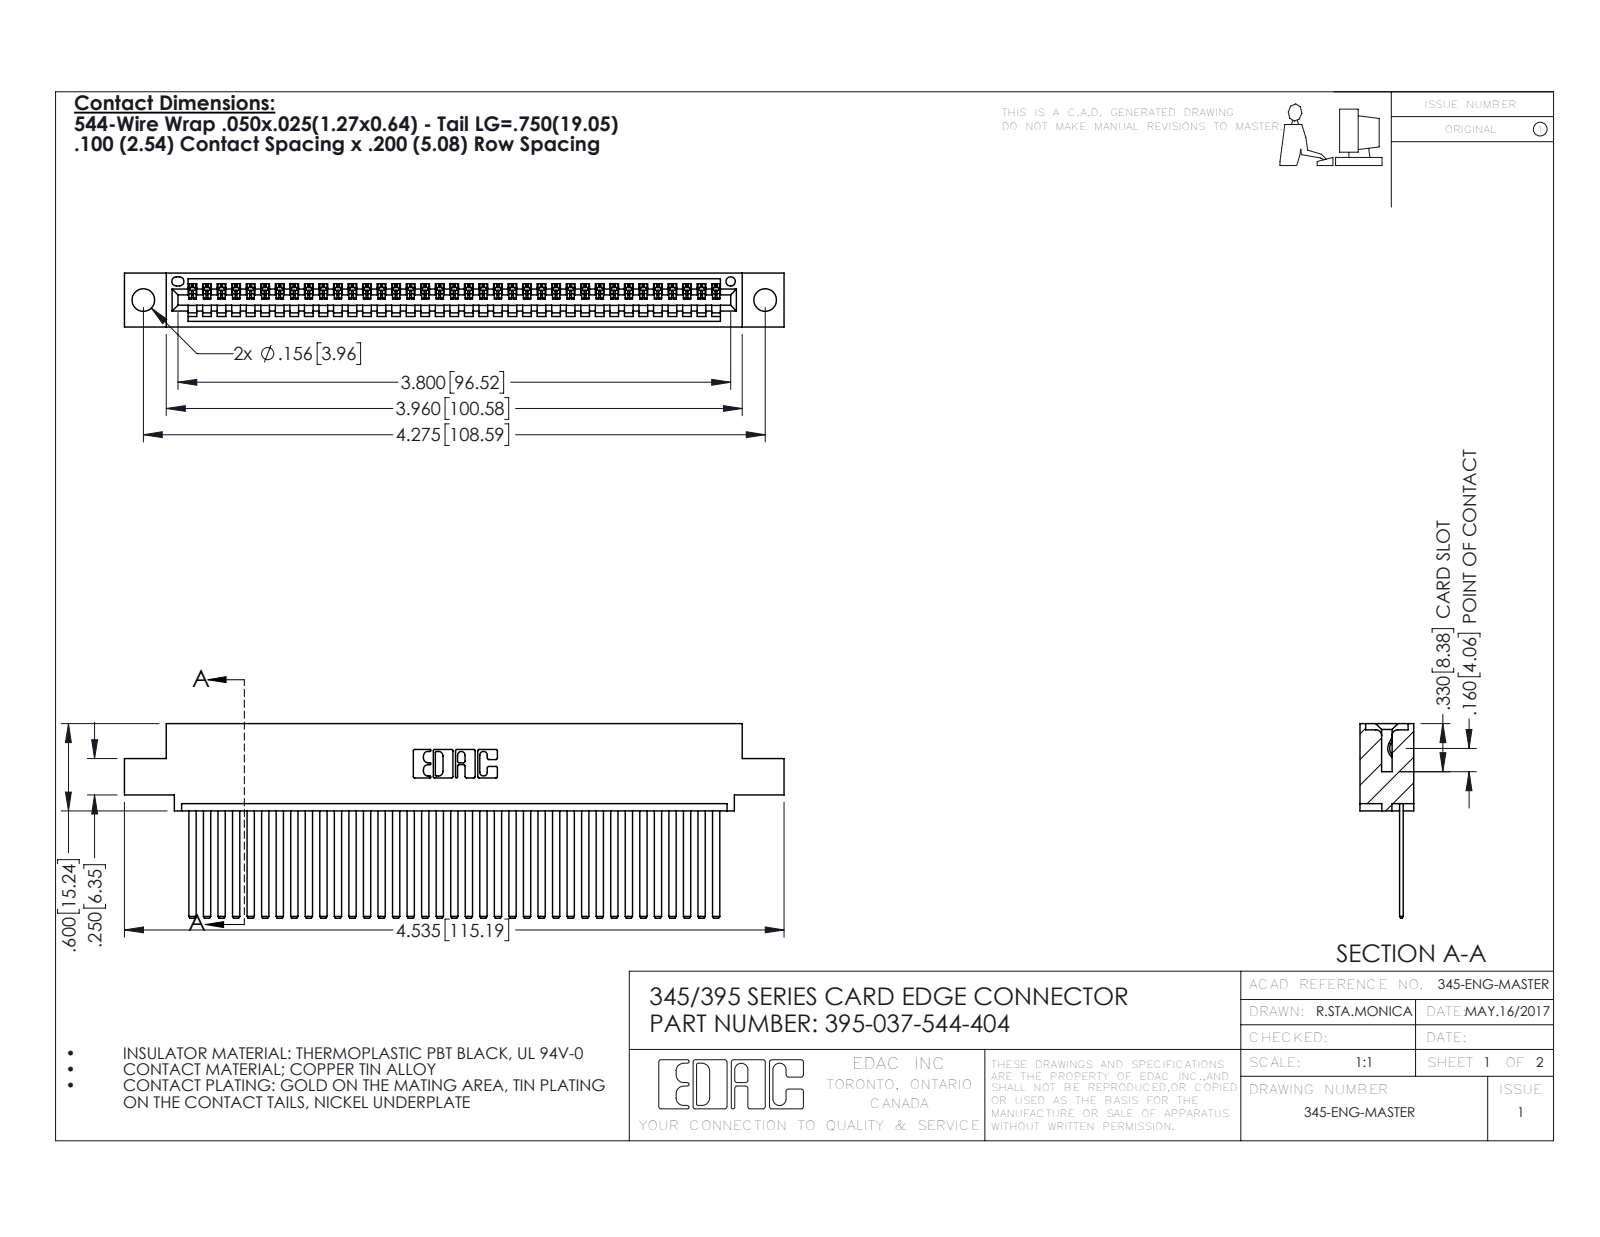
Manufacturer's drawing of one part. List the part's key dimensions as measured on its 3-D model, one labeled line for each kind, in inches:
Part name (STEP PRODUCT): 395-037-544-404; 345-292-001_345-293-144; 345 Part_0.110 Offset - 0.156 Dia-TH
STEP written by: SolidWorks 2016 (CONFIG_CONTROL_DESIGN)
Units: inches
Bodies: 38 solids, 2054 faces (1416 planar, 638 cylindrical, 0 other)
Overall size (bounding box): 4.535 × 1.337 × 0.37
Volume: 0.681 in³ · Surface area: 24.72 in²
Round holes (diameter × count): ⌀0.156 ×2, ⌀0.064 ×1
Partial cylindrical surfaces — rounded edges, fillets, slot ends (radius × count): R0.006 ×74, R0.01 ×22, R0.007 ×6, R0.031 ×6, R0.026 ×3, R0.031 ×2, R0.04 ×2, R0.014 ×1
Main face-to-face distances: 0.072, 0.298, 0.025, 0.098, 0.272, 0.37, 0.2, 0.225, 0.149, 0.072
Hole centre spacings: 0.27, 4.039, 4.275
